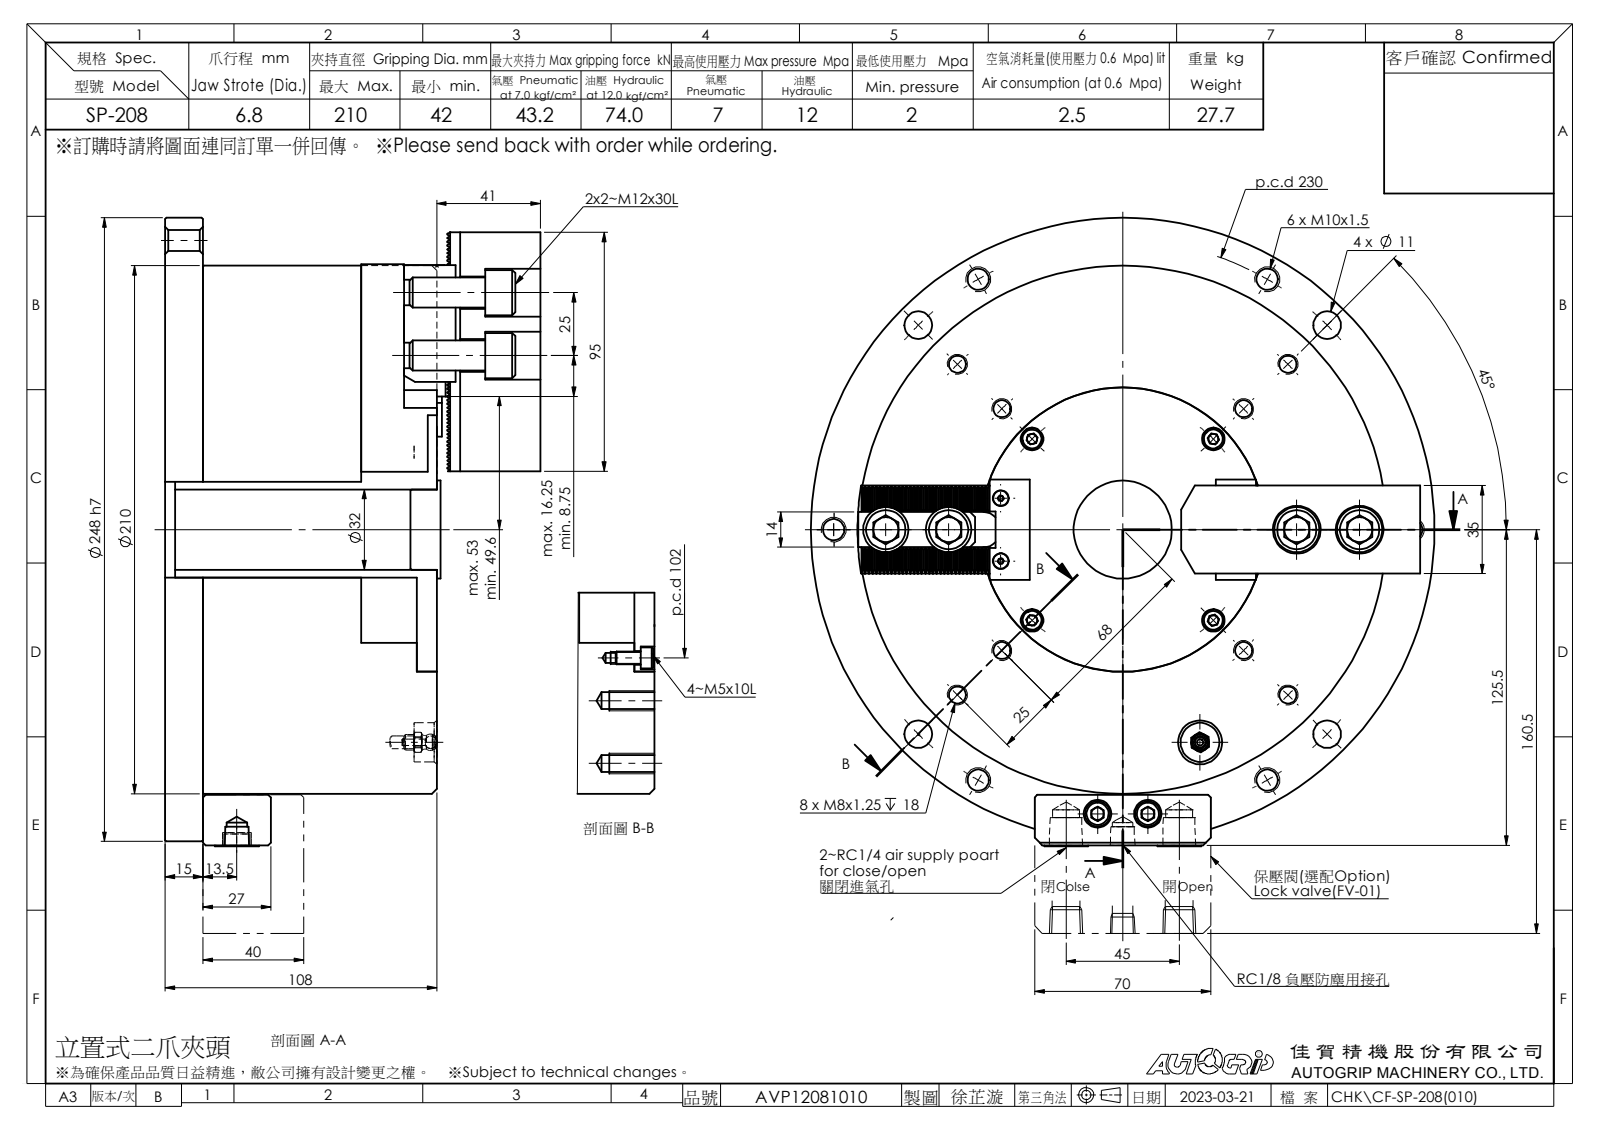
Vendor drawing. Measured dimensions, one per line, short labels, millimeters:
name: SJ-08; 圓頭內六角螺栓_M5x10; CF-SP-308-09000; CF-SP-208-01010 (+8 more)
written by: SolidWorks 2020 (CONFIG_CONTROL_DESIGN)
unit: mm
bodies: 32 solids, 2478 faces (1637 planar, 621 cylindrical, 220 other)
size: 250 × 248 × 149.25
volume: 4 032 000 mm³; area: 420 496 mm²
holes: 8× ⌀6.8, 6× ⌀8.5, 6× ⌀11, 4× ⌀2.4, 4× ⌀3.4, 4× ⌀4.1, 4× ⌀5, 4× ⌀5.5, 4× ⌀9, 4× ⌀10.2, 4× ⌀13, 4× ⌀19
bosses: 7× ⌀6, 5× ⌀3, 4× ⌀18, 4× ⌀12, 4× ⌀8.5, 4× ⌀5, 2× ⌀17.5, 2× ⌀11.5
rounds: 196× R0.1, 2× R7, 2× R105, 1× R45
face distances: 15, 108, 93, 30, 35, 78, 63, 22, 100, 85
hole spacings: 115, 84.99, 106.06, 115.2, 125.8, 133.6, 147.9, 25
